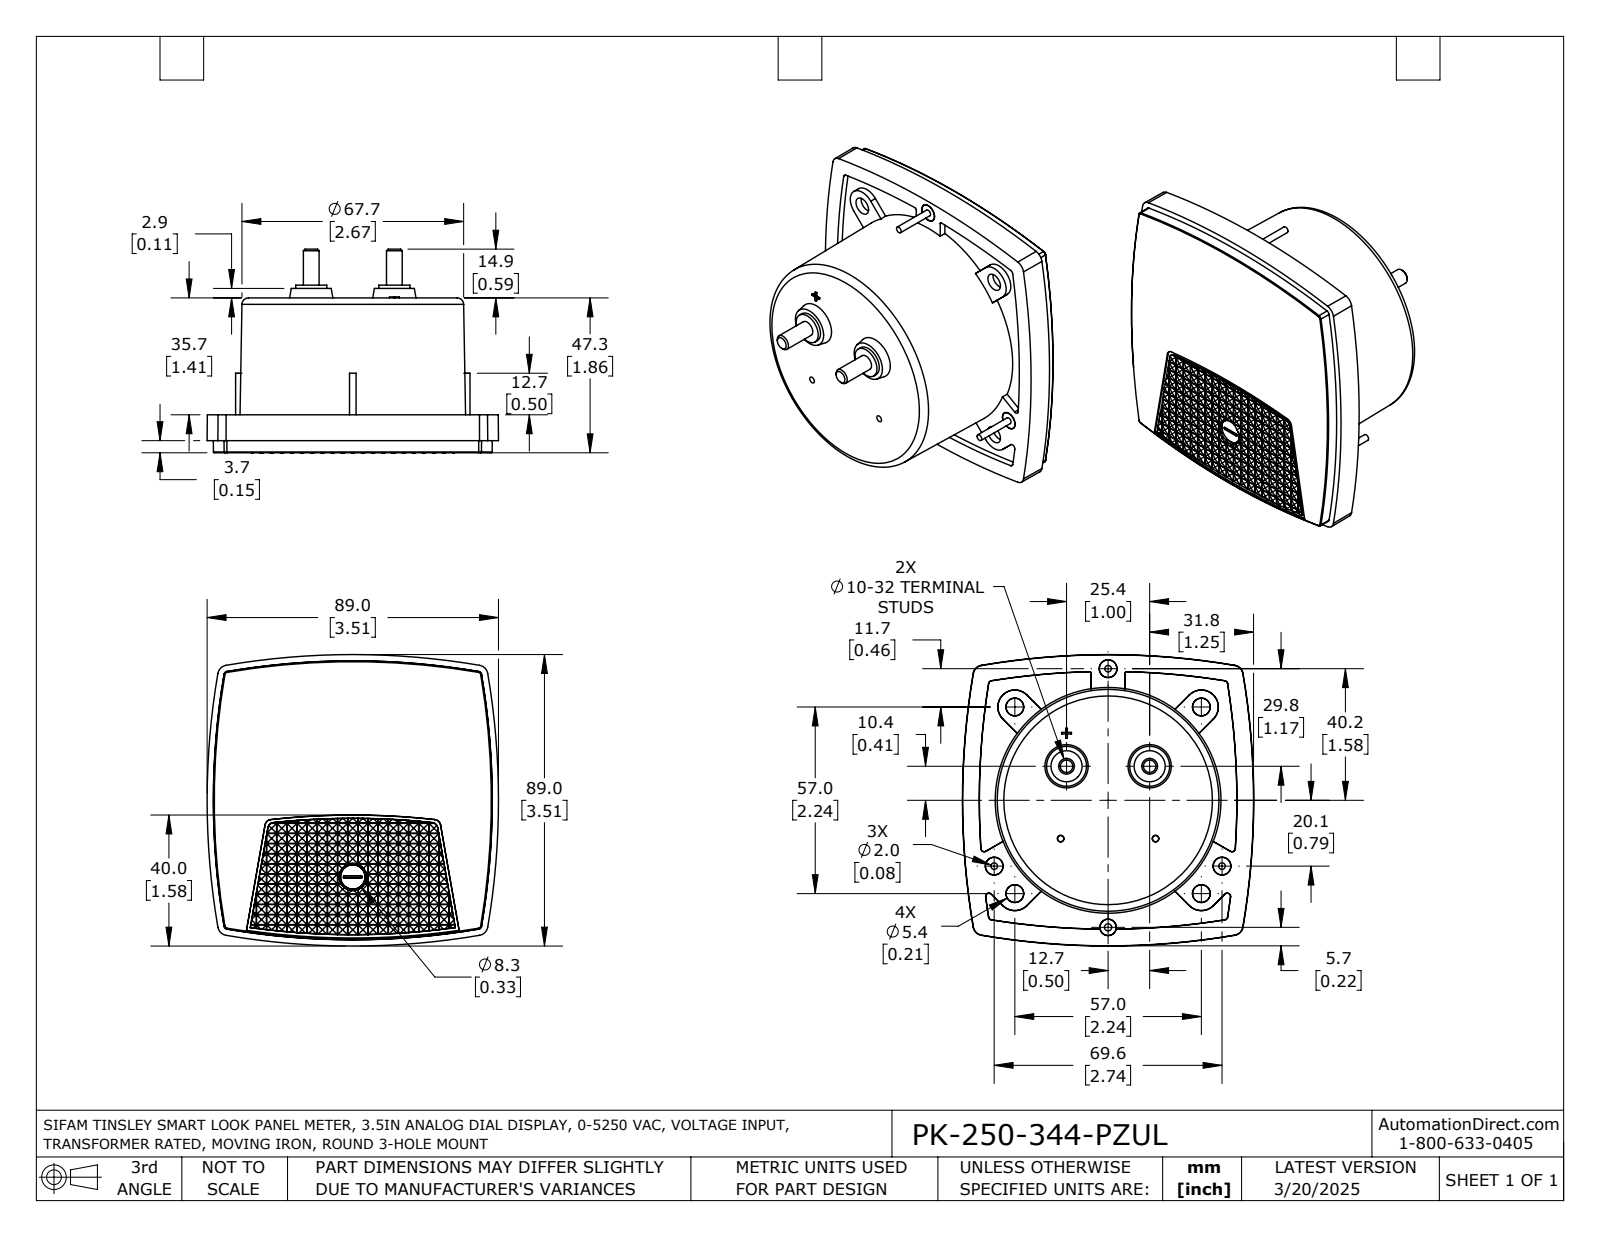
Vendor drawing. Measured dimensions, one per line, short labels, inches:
name: PK-250-344-PZUL
written by: SolidWorks 2021 (AUTOMOTIVE_DESIGN)
unit: in
bodies: 1 solid, 1078 faces (950 planar, 23 cylindrical, 105 other)
size: 3.505 × 3.505 × 2.453
volume: 12.99 in³; area: 44.29 in²
holes: 1× ⌀0.087
bosses: 3× ⌀0.213, 3× ⌀0.079, 2× ⌀0.374, 2× ⌀0.189
rounds: 1× R8.961
face distances: 1.862, 1.406, 0.457, 0.079, 1.484, 0.378, 0.024, 0.096, 0.072, 0.12
